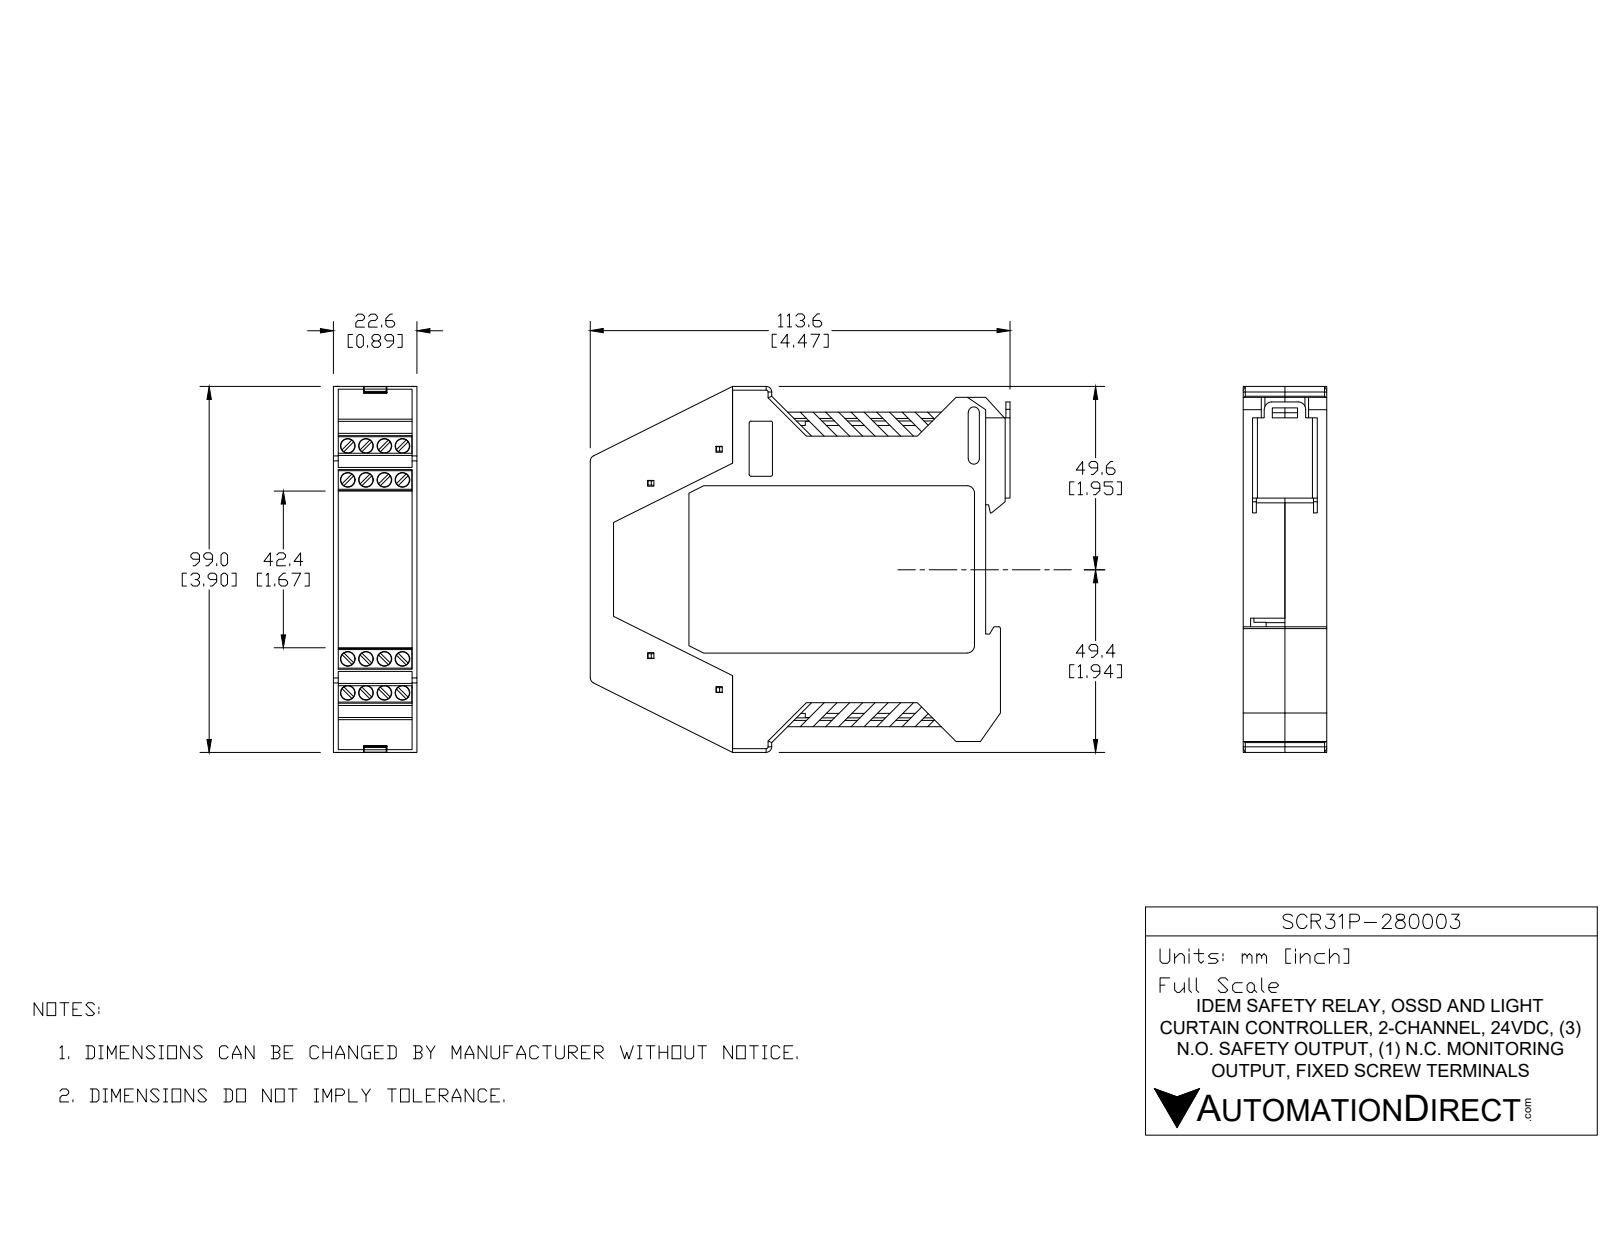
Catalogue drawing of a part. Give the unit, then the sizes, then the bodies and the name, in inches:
Units: inches
Overall size (bounding box): 4.472 × 3.898 × 0.89
Round holes (diameter × count): ⌀0.157 ×16, ⌀0.079 ×2
Round bosses / shafts (diameter × count): ⌀0.15 ×16, ⌀0.055 ×16, ⌀0.075 ×2
Partial cylindrical surfaces — rounded edges, fillets, slot ends (radius × count): R0.02 ×39, R0.012 ×24, R0.008 ×18, R0.059 ×6, R0.026 ×4, R0.031 ×4, R0.079 ×4, R0.051 ×2
Main face-to-face distances: 0.831, 0.051, 0.059, 0.823, 0.882, 0.772, 0.89, 0.043, 0.445, 0.437
Hole centre spacings: 0.193, 0.362, 0.39, 0.41, 0.532, 2.268, 2.276, 2.301
Volume: 3.949 in³ · Surface area: 107.4 in²
Bodies: 10 solids, 1899 faces (1607 planar, 280 cylindrical, 12 other)
Part name (STEP PRODUCT): 280-Viper-22
STEP written by: SolidWorks 2019 (AUTOMOTIVE_DESIGN)
